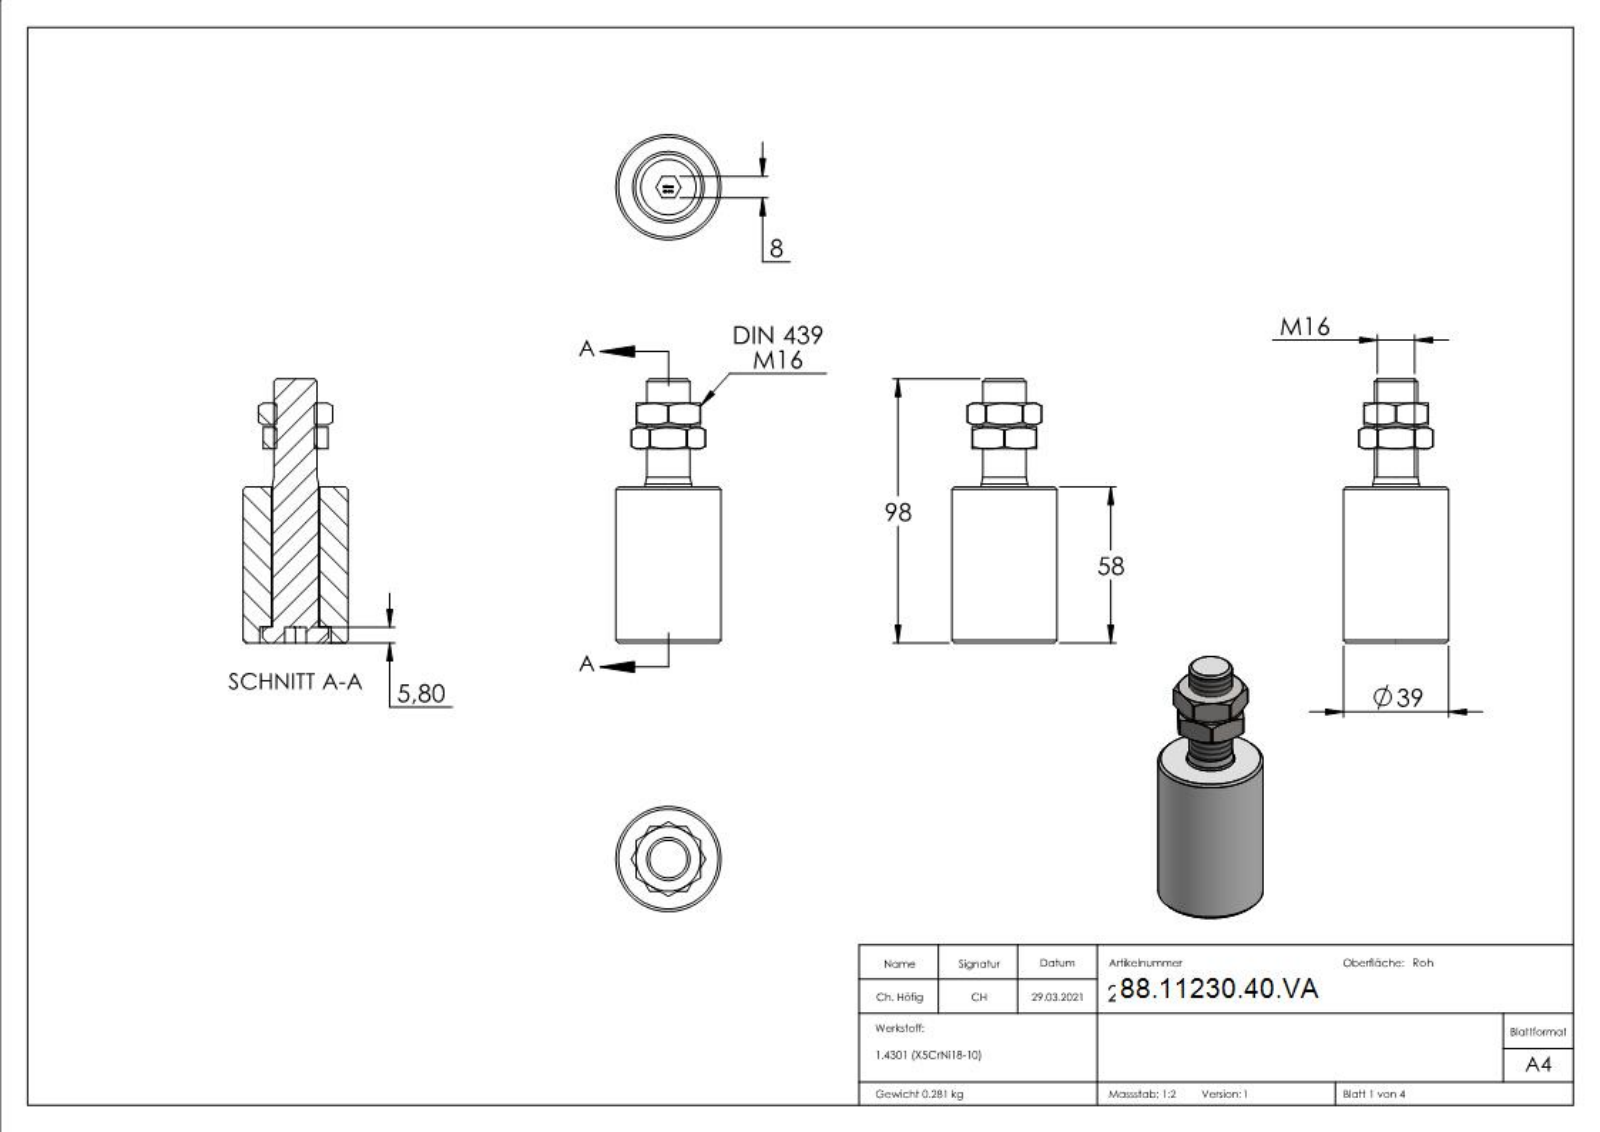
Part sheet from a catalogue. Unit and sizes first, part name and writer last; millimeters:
Units: millimetres
Overall size (bounding box): 22000 × 14000 × 14000
Round holes (diameter × count): ⌀14 ×1, ⌀18 ×1, ⌀26.5 ×1
Round bosses / shafts (diameter × count): ⌀39 ×1, ⌀24.5 ×1, ⌀17.15 ×1, ⌀16 ×1
Partial cylindrical surfaces — rounded edges, fillets, slot ends (radius × count): R0.5 ×12
Main face-to-face distances: 58, 8, 9, 24, 6, 52, 17, 1, 72, 80
Volume: 80 518 mm³ · Surface area: 21 783 mm²
Bodies: 4 solids, 315 faces (155 planar, 28 cylindrical, 132 other)
Part name (STEP PRODUCT): 230-40-VA; DIN 439 M4-M20_DIN 439 M16; DIN 439 M4-M20; 230-xx-VA Teil2_230-40-VA Teil2 (+3 more)
STEP written by: SolidWorks 2018 (CONFIG_CONTROL_DESIGN)
